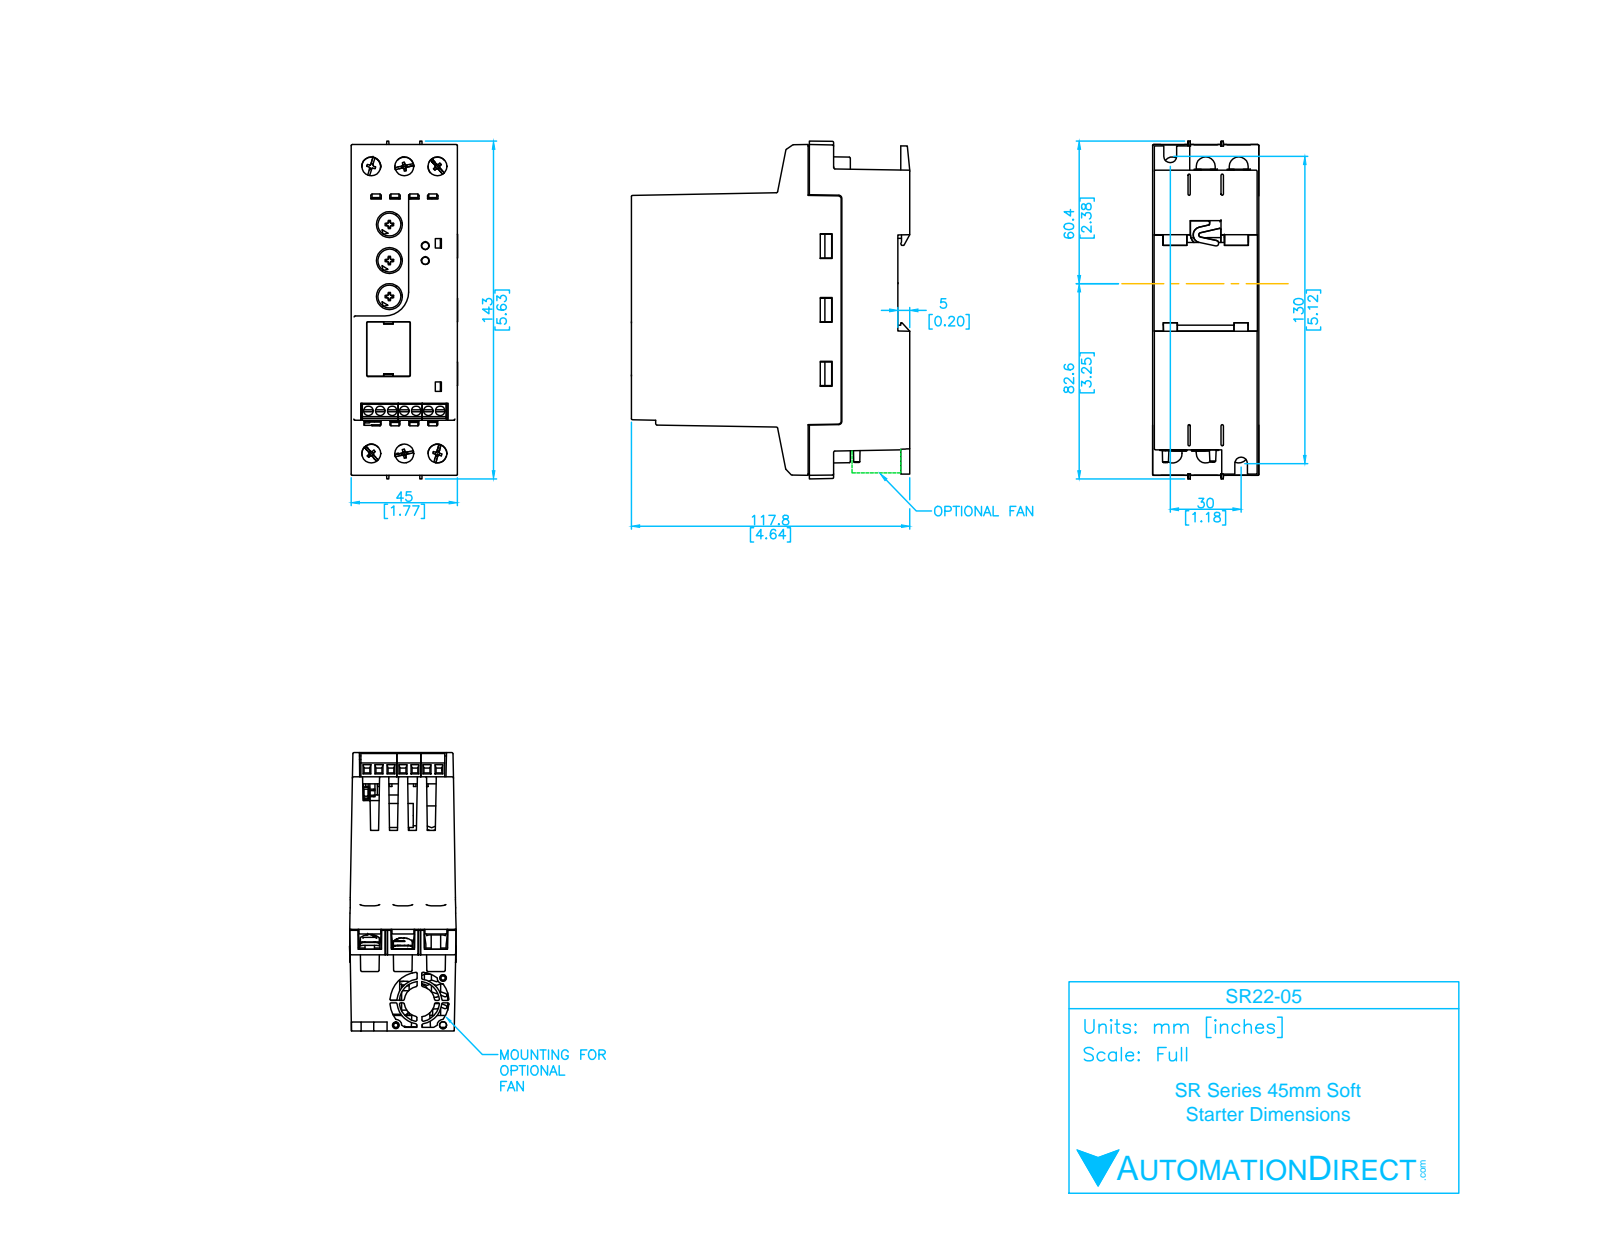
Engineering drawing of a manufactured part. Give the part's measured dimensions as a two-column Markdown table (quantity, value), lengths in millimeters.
| quantity | value |
| --- | --- |
| part name | SR22-05 |
| STEP written by | SolidWorks 2013 (AUTOMOTIVE_DESIGN) |
| units | millimeters |
| bodies | 1 solid, 567 faces (437 planar, 98 cylindrical, 32 other) |
| overall size | 144 × 117.8 × 45.64 |
| volume | 572 724 mm³ |
| surface area | 56 020 mm² |
| round holes (diameter × count) | 9.5 × 6, 3.5 × 5, 11.3 × 3, 4 × 2 |
| round bosses / shafts (diameter × count) | 10.44 × 3 |
| partial cylindrical surfaces (radius × count) | 0.5 × 36, 4.88 × 6, 1 × 2, 2.75 × 2, 10 × 1 |
| main face-to-face distances | 45, 44.98, 44.96, 117.8, 0.5, 5.14, 112.66, 1.5, 116.3, 111.16 |
| hole center spacings | 5.25, 13, 123.69, 10.5, 123, 15, 15.75, 26 |
